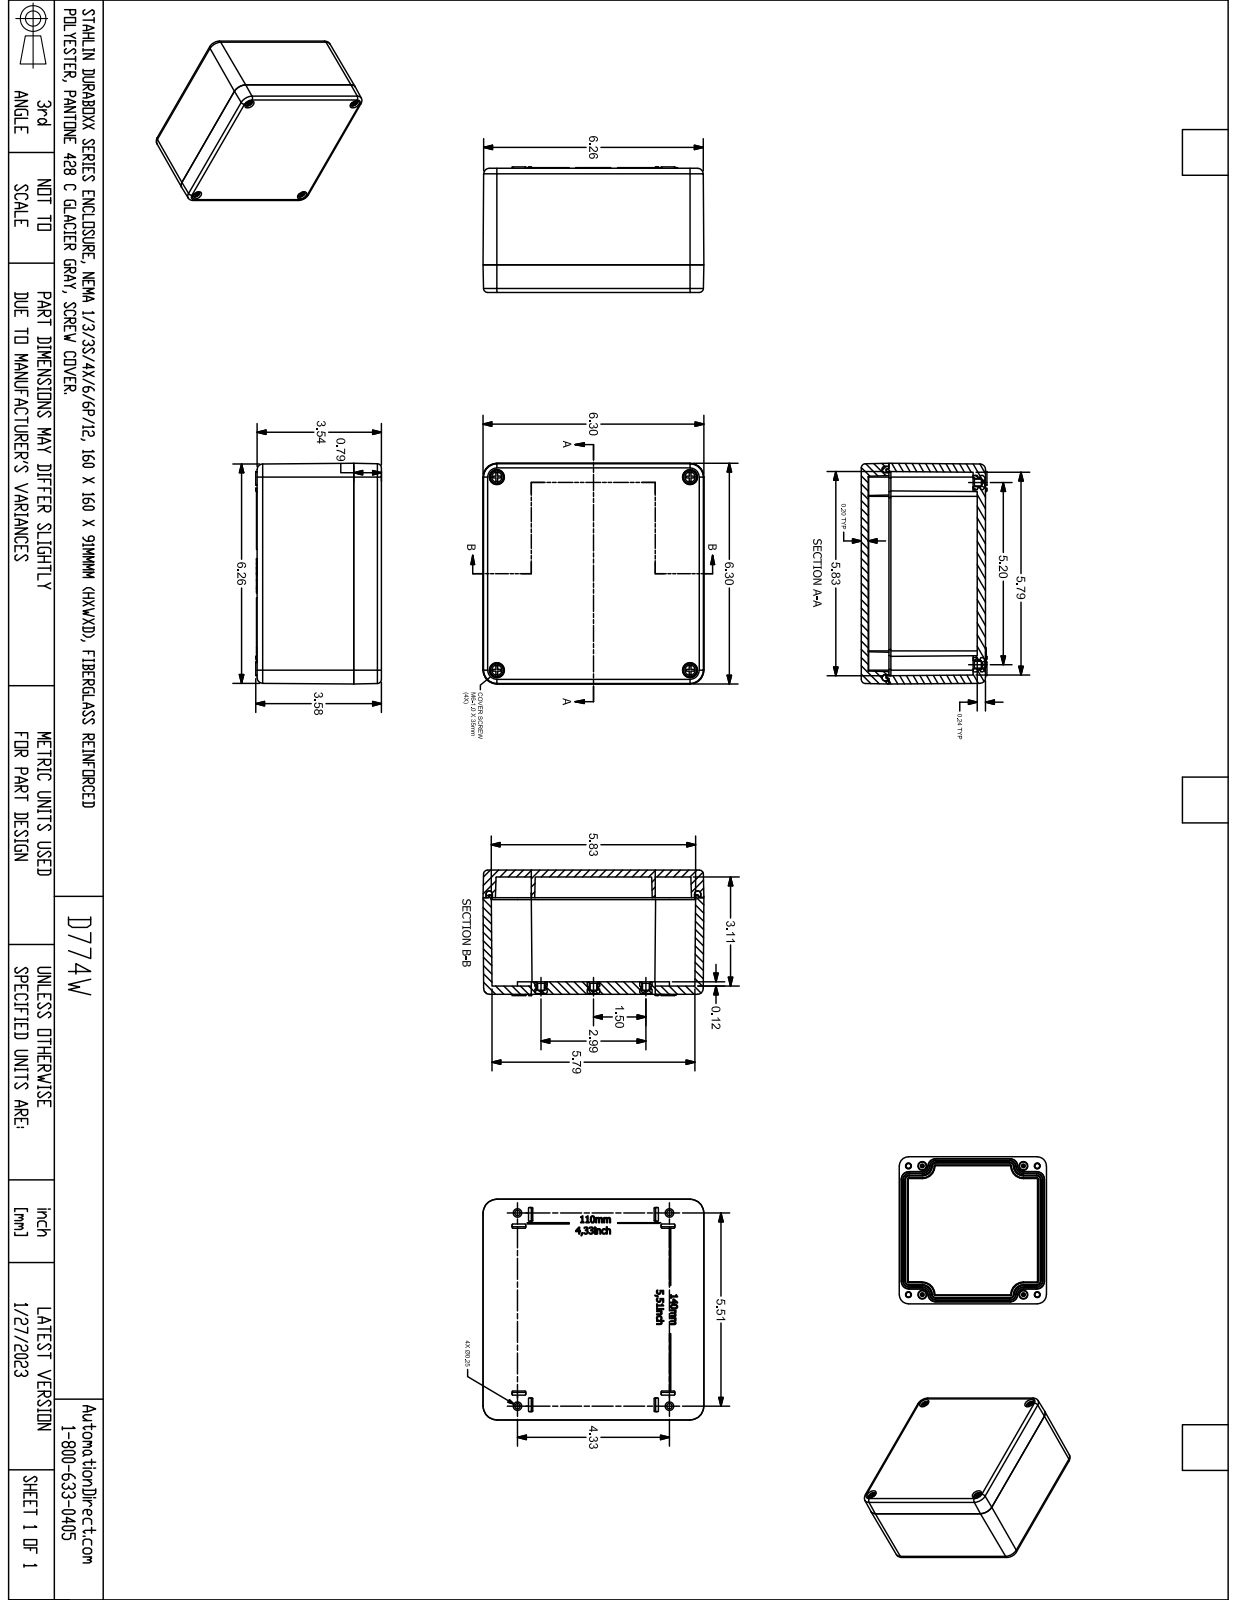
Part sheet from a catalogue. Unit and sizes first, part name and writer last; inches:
Units: inches
Overall size (bounding box): 6.299 × 6.299 × 3.583
Round holes (diameter × count): ⌀0.194 ×6, ⌀0.236 ×6, ⌀0.194 ×4, ⌀0.213 ×4, ⌀0.276 ×4
Round bosses / shafts (diameter × count): ⌀0.291 ×10, ⌀0.374 ×4, ⌀0.315 ×4, ⌀0.236 ×4, ⌀0.205 ×4
Partial cylindrical surfaces — rounded edges, fillets, slot ends (radius × count): R0.02 ×32, R0.089 ×12, R0.167 ×8, R0.344 ×8, R0.016 ×6, R0.118 ×4, R0.128 ×4, R0.128 ×4
Main face-to-face distances: 0.236, 3.543, 3.346, 0.197, 3.307, 3.11, 0.787, 2.756, 0.591, 2.52
Hole centre spacings: 1.27, 1.496, 2.76, 4.255, 5.408, 5.5, 5.512, 6.022
Volume: 41.89 in³ · Surface area: 382 in²
Bodies: 17 solids, 1254 faces (654 planar, 170 cylindrical, 430 other)
Part name (STEP PRODUCT): DU774W
STEP written by: SolidWorks 2018 (AUTOMOTIVE_DESIGN)
